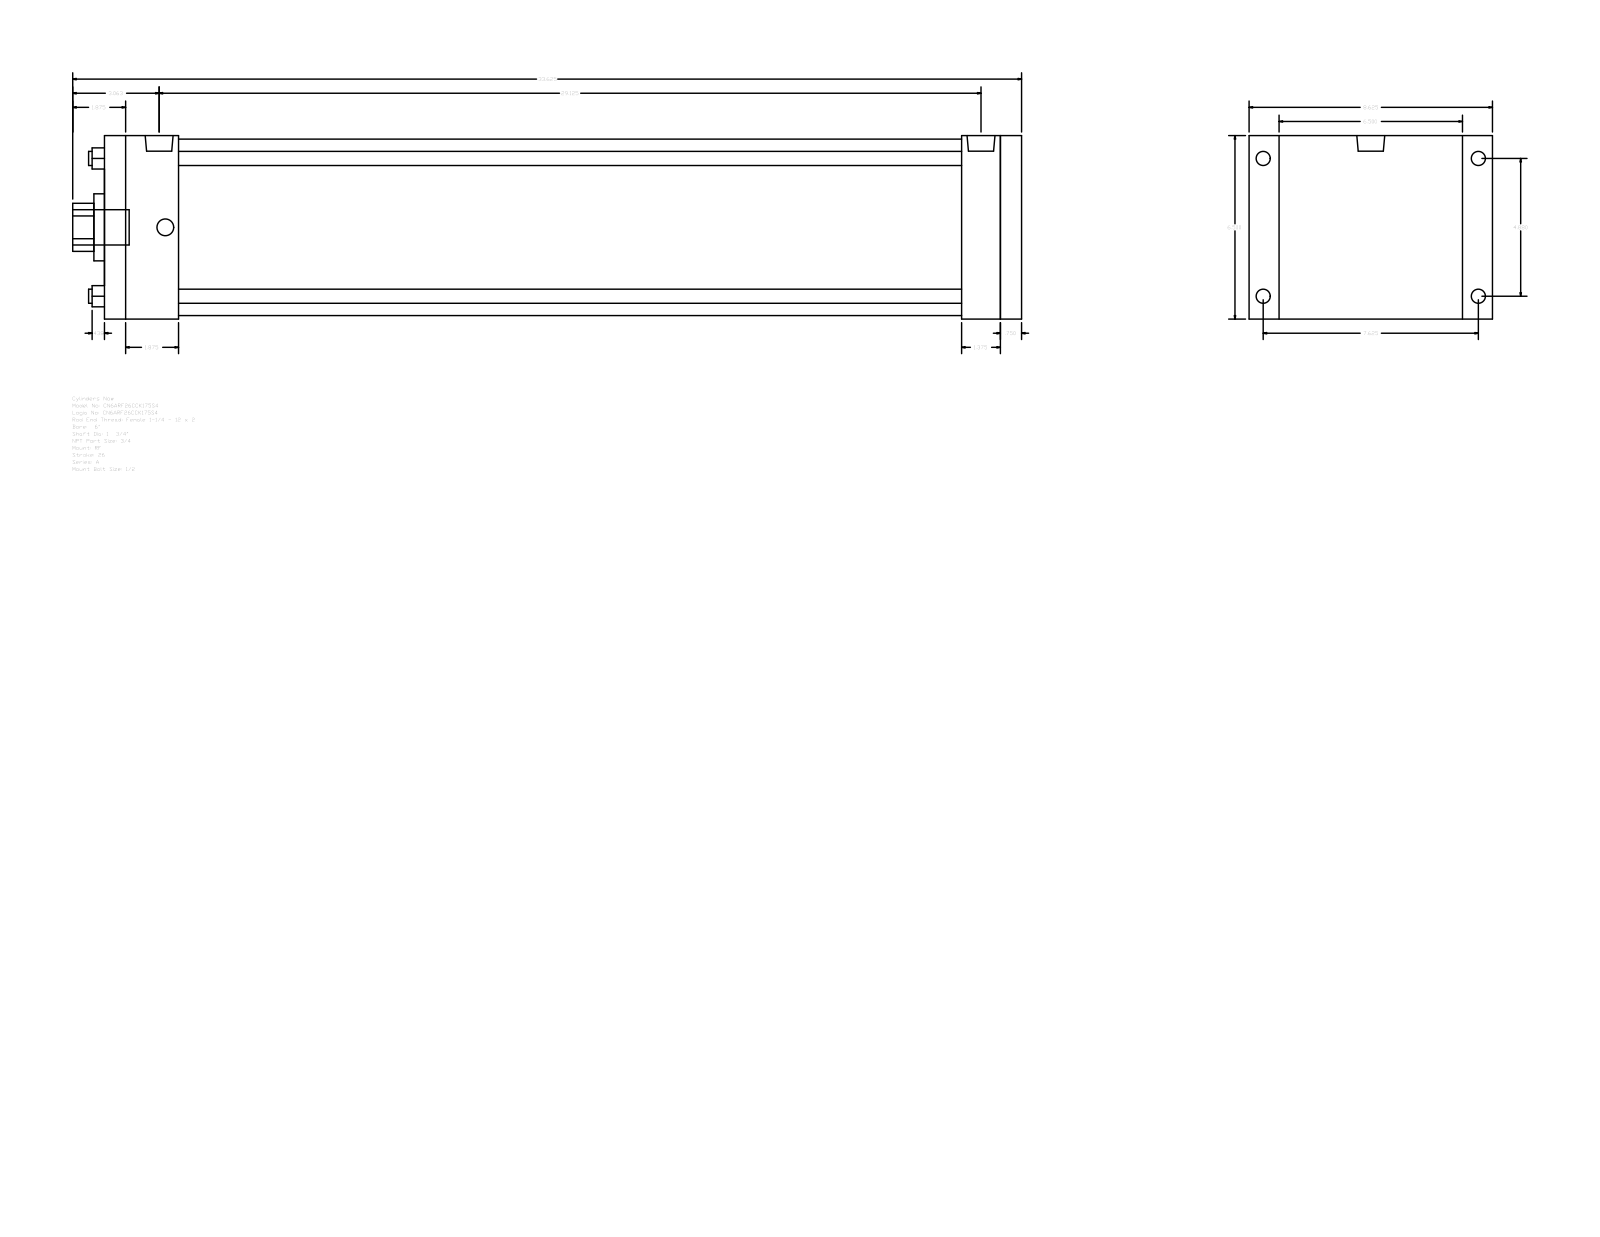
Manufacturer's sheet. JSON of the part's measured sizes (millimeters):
{"part_name": "A_RF__0600_1.75", "step_written_by": "GSSL Pune (CONFIG_CONTROL_DESIGN)", "units": "millimeters", "bodies": {"solids": 0, "faces": 92, "planar": 64, "cylindrical": 28, "other": 0}, "overall_size": [854.08, 219.07, 165.1], "round_holes": [[12.7, 4], [44.45, 1], [60.33, 1], [158.75, 1]], "round_bosses_or_shafts": [[15.08, 4], [12.7, 4], [25.12, 2], [31.75, 1]], "partial_cylinders_radius": [[21.63, 1]], "face_to_face_distances": [165.1, 825.51, 806.45, 19.06, 34.92, 66.68, 739.77, 758.83, 771.53, 704.85], "hole_center_spacings": [87.65, 123.96, 175.31]}
